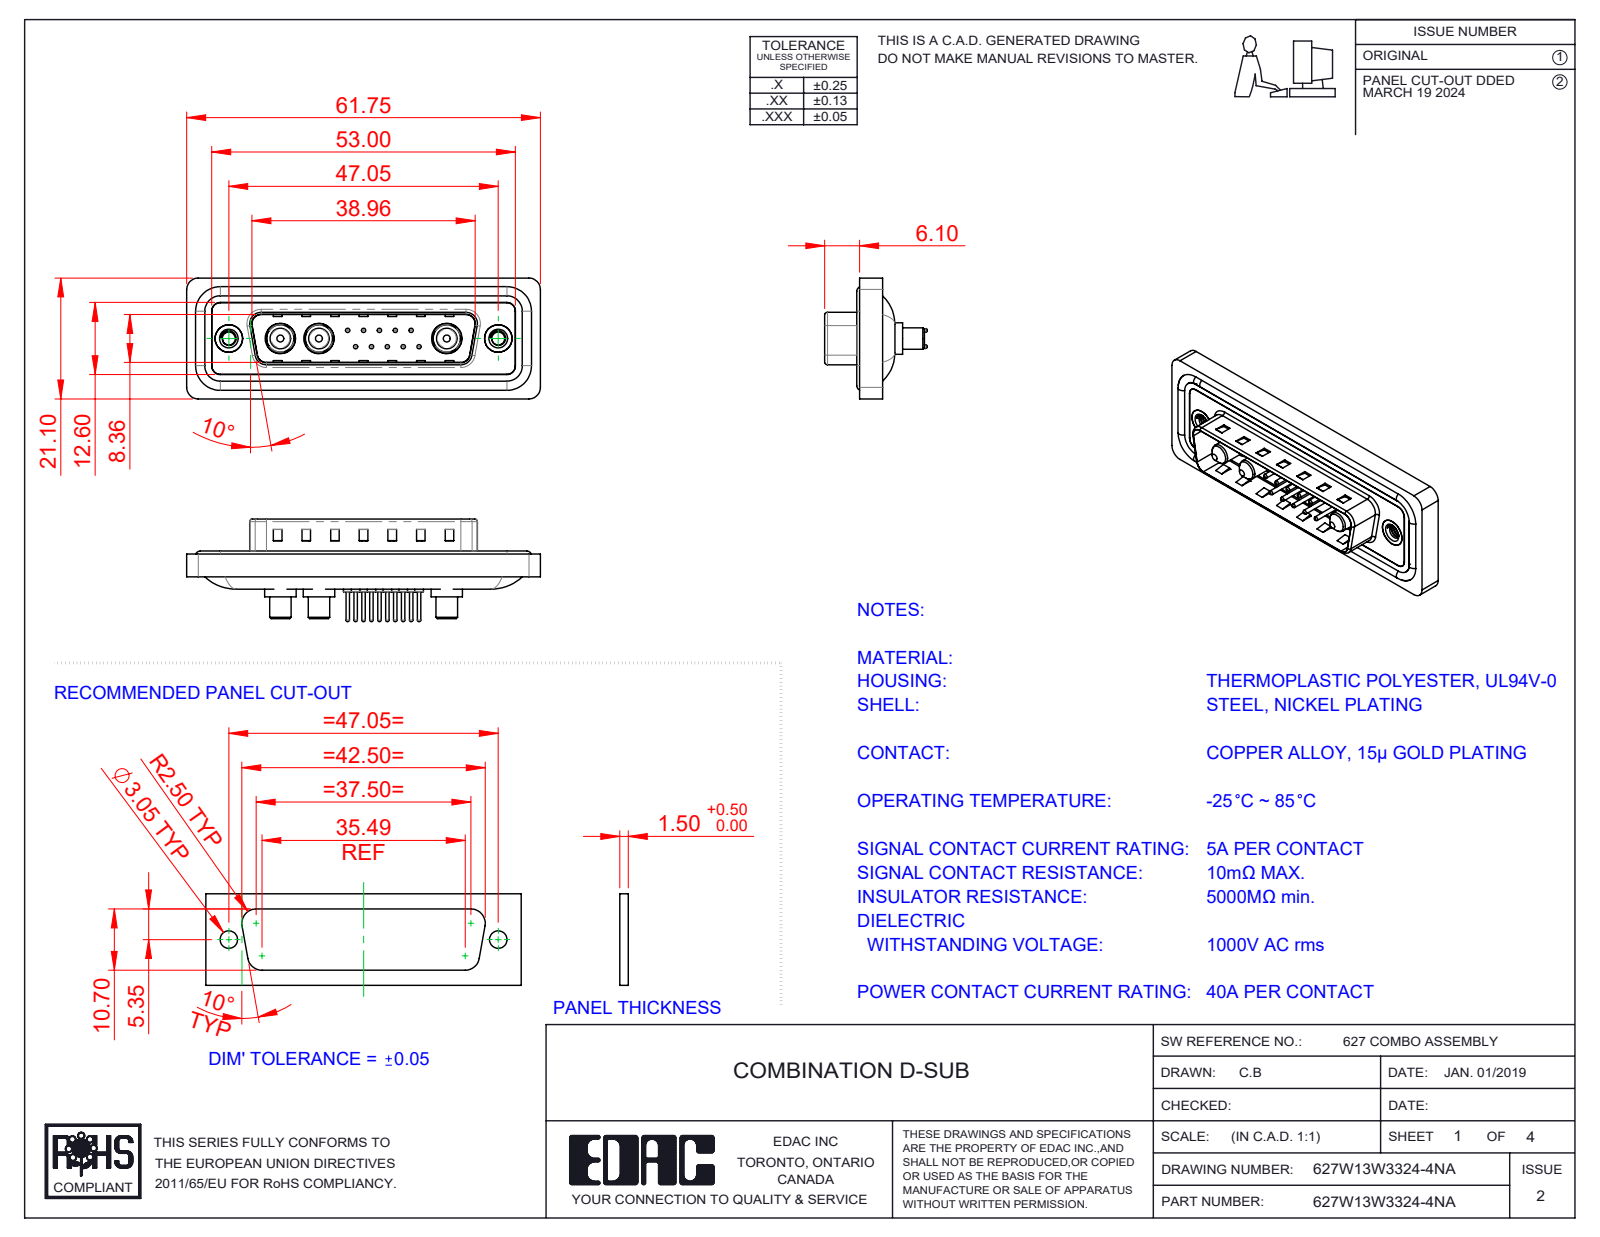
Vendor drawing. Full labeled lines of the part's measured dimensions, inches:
Part name (STEP PRODUCT): 627Combo Contact Row 2_24; 627Combo Waterproof Housing_25 Contacts; 627Combo Threaded Rivet_A; 627W13W3324-4NA (+5 more)
STEP written by: SolidWorks 2023 (CONFIG_CONTROL_DESIGN)
Units: inches
Bodies: 23 solids, 968 faces (309 planar, 387 cylindrical, 272 other)
Overall size (bounding box): 2.431 × 0.831 × 0.705
Volume: 0.451 in³ · Surface area: 18.45 in²
Round holes (diameter × count): ⌀0.03 ×10, ⌀0.063 ×10, ⌀0.079 ×10, ⌀0.191 ×3, ⌀0.209 ×3, ⌀0.089 ×2, ⌀0.157 ×2, ⌀0.189 ×2, ⌀0.197 ×2
Round bosses / shafts (diameter × count): ⌀0.059 ×10, ⌀0.024 ×10, ⌀0.063 ×4, ⌀0.217 ×3, ⌀0.205 ×3, ⌀0.187 ×3, ⌀0.148 ×3, ⌀0.142 ×3
Partial cylindrical surfaces — rounded edges, fillets, slot ends (radius × count): R0.059 ×22, R0.079 ×18, R0.02 ×8, R0.063 ×8, R0.01 ×4, R0.024 ×4, R0.026 ×4, R0.035 ×4
Main face-to-face distances: 0.016, 0.059, 0.043, 0.063, 0.02, 0.122, 0.114, 0.032, 0.377, 0.161
Hole centre spacings: 0.124, 0.109, 0.198, 0.218, 0.295, 0.198, 0.327, 0.398
